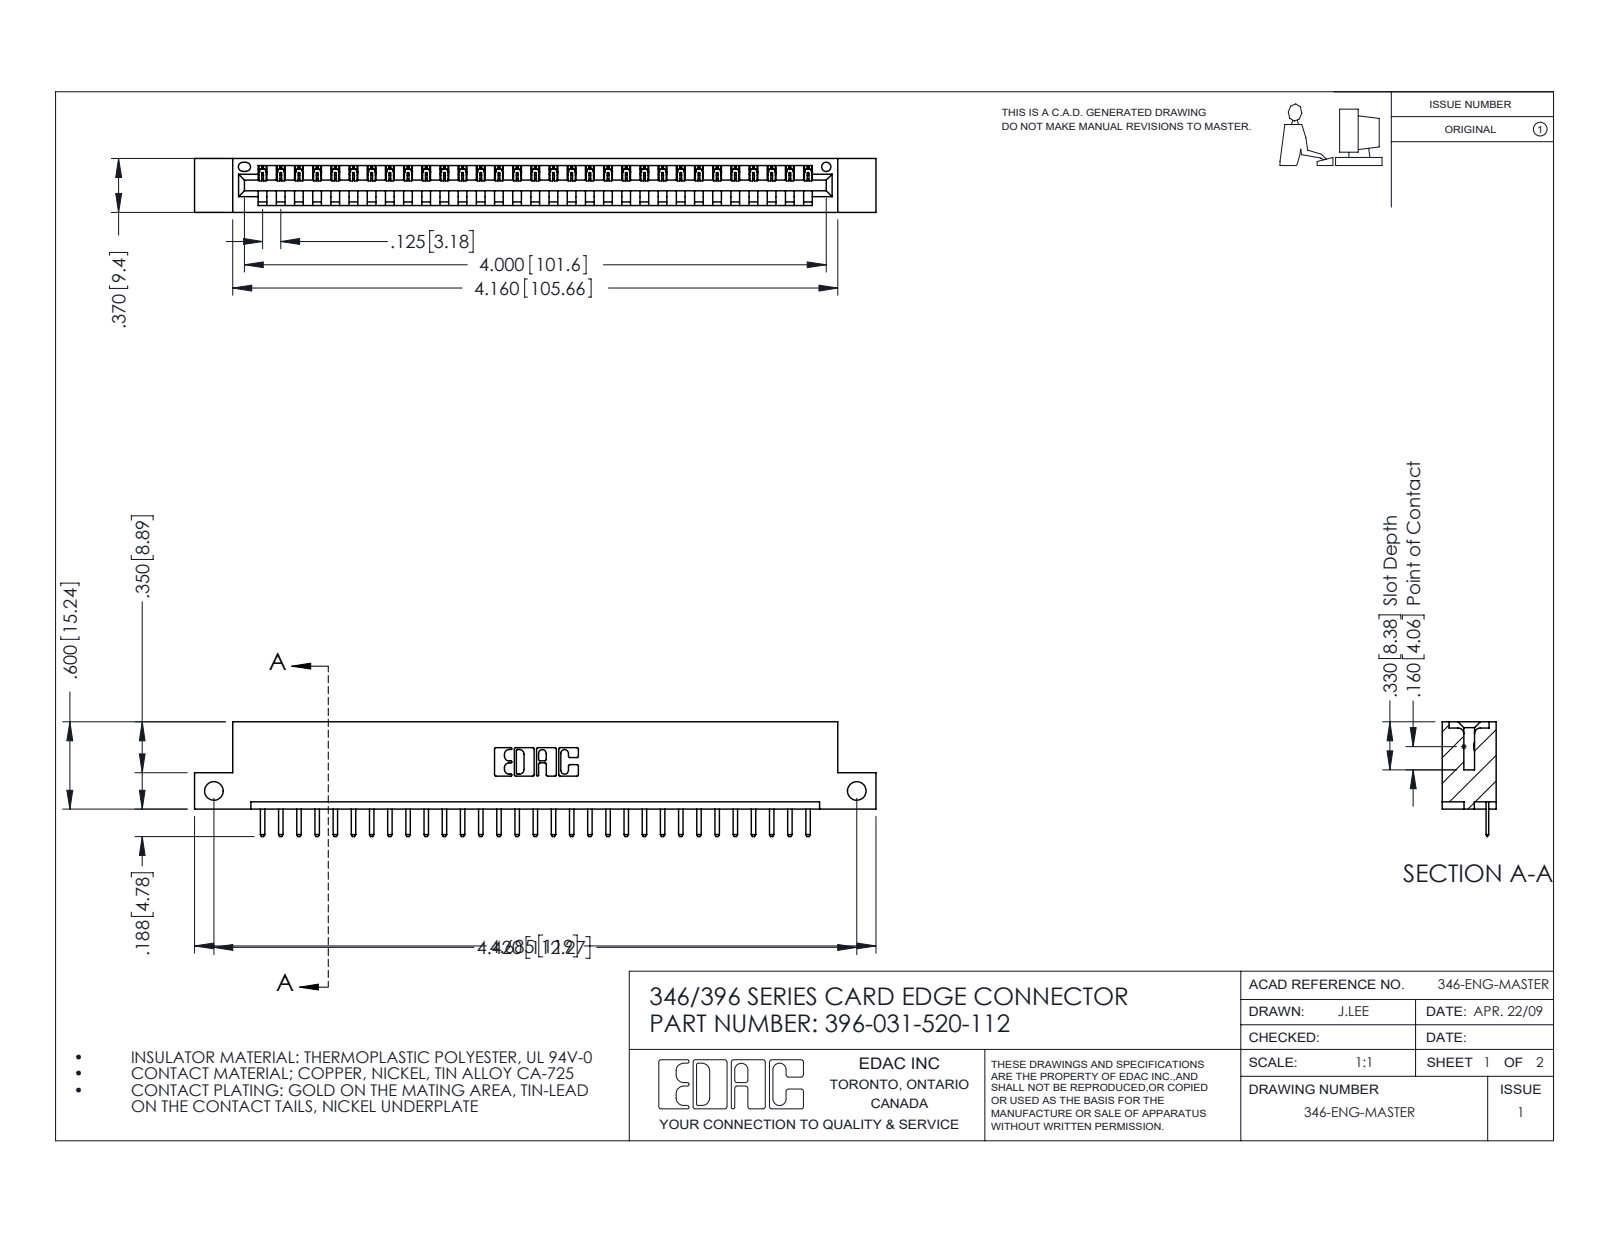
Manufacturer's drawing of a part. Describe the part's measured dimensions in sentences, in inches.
The part is named "345-292-001_345-293-120; 346 Part_Flush Mounting Lugs - Side Mount; 396-031-520-112". Its 3-D file was written by "SolidWorks 2016 (CONFIG_CONTROL_DESIGN)". It is 32 solids with 2044 faces: 1378 planar, 666 cylindrical and 0 other. Overall it measures 4.685 by 0.788 by 0.37 inches. Its volume is 0.68 cubic inches and its surface area 20.71 square inches. Round holes: 2 of diameter 0.128, 1 of diameter 0.064. Partial cylindrical surfaces (rounded edges, fillets, slot ends): 64 of radius 0.01, 62 of radius 0.006, 22 of radius 0.01, 6 of radius 0.007, 6 of radius 0.031, 3 of radius 0.026, 2 of radius 0.031, 2 of radius 0.04. The main face-to-face distances are 0.048, 0.322, 0.37, 0.25, 0.148, 0.222, 0.1, 0.174, 0.072, 0.298. The hole center spacings are 4.42.
